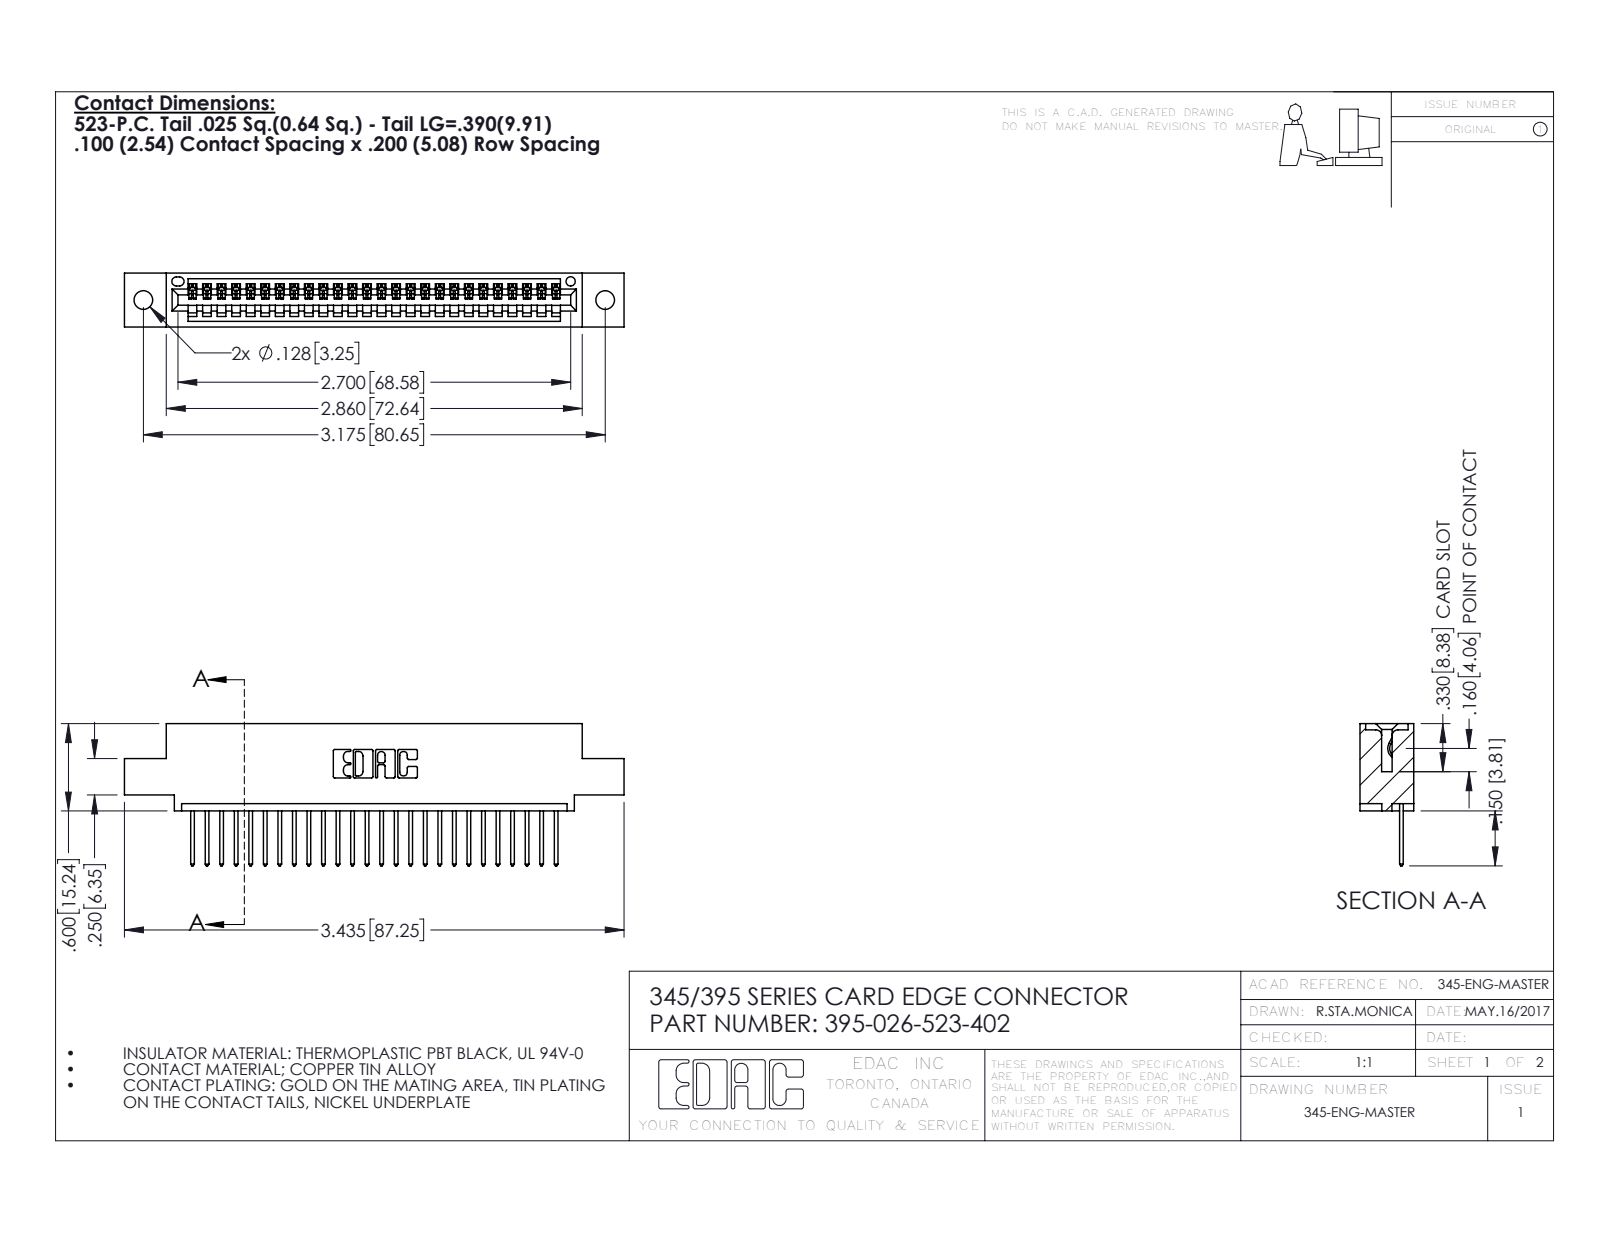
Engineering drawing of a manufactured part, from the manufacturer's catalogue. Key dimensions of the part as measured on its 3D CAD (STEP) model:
Part name (STEP PRODUCT): 345-292-001_345-293-123; 345 Part_0.110 Offset - 0.128 Dia; 395-026-523-402
STEP written by: SolidWorks 2016 (CONFIG_CONTROL_DESIGN)
Units: inches
Bodies: 27 solids, 1638 faces (1124 planar, 514 cylindrical, 0 other)
Overall size (bounding box): 3.435 × 0.977 × 0.37
Volume: 0.49 in³ · Surface area: 15.97 in²
Round holes (diameter × count): ⌀0.128 ×2, ⌀0.064 ×1
Partial cylindrical surfaces — rounded edges, fillets, slot ends (radius × count): R0.006 ×52, R0.01 ×52, R0.01 ×22, R0.007 ×6, R0.031 ×6, R0.026 ×3, R0.031 ×2, R0.04 ×2
Main face-to-face distances: 0.298, 0.072, 0.37, 0.2, 0.098, 0.272, 0.025, 0.225, 0.149, 0.072
Hole centre spacings: 0.27, 2.94, 3.175
